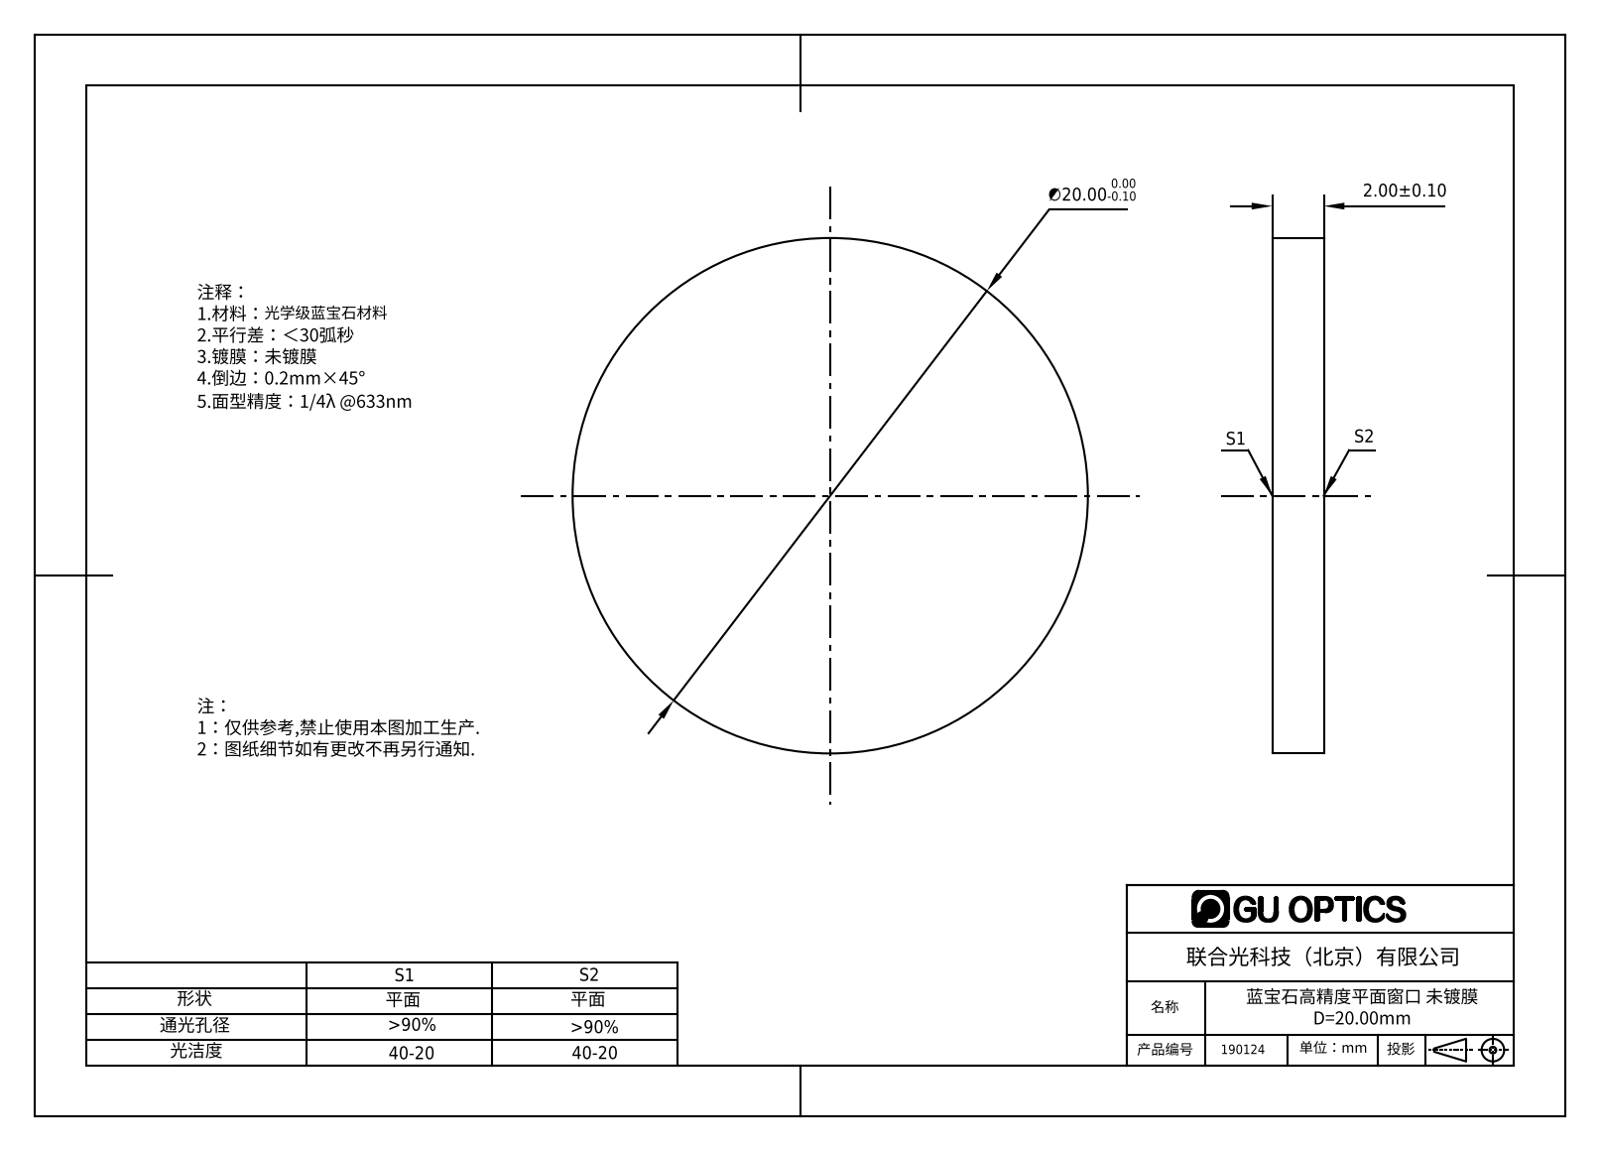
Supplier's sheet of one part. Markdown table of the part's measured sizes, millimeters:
| quantity | value |
| --- | --- |
| part name | 190124 |
| STEP written by | SolidWorks 2016 (AUTOMOTIVE_DESIGN) |
| units | millimeters |
| bodies | 1 solid, 4 faces (2 planar, 2 cylindrical, 0 other) |
| overall size | 20 × 20 × 2 |
| volume | 628 mm³ |
| surface area | 754 mm² |
| round bosses / shafts (diameter × count) | 20 × 1 |
| main face-to-face distances | 2 |
